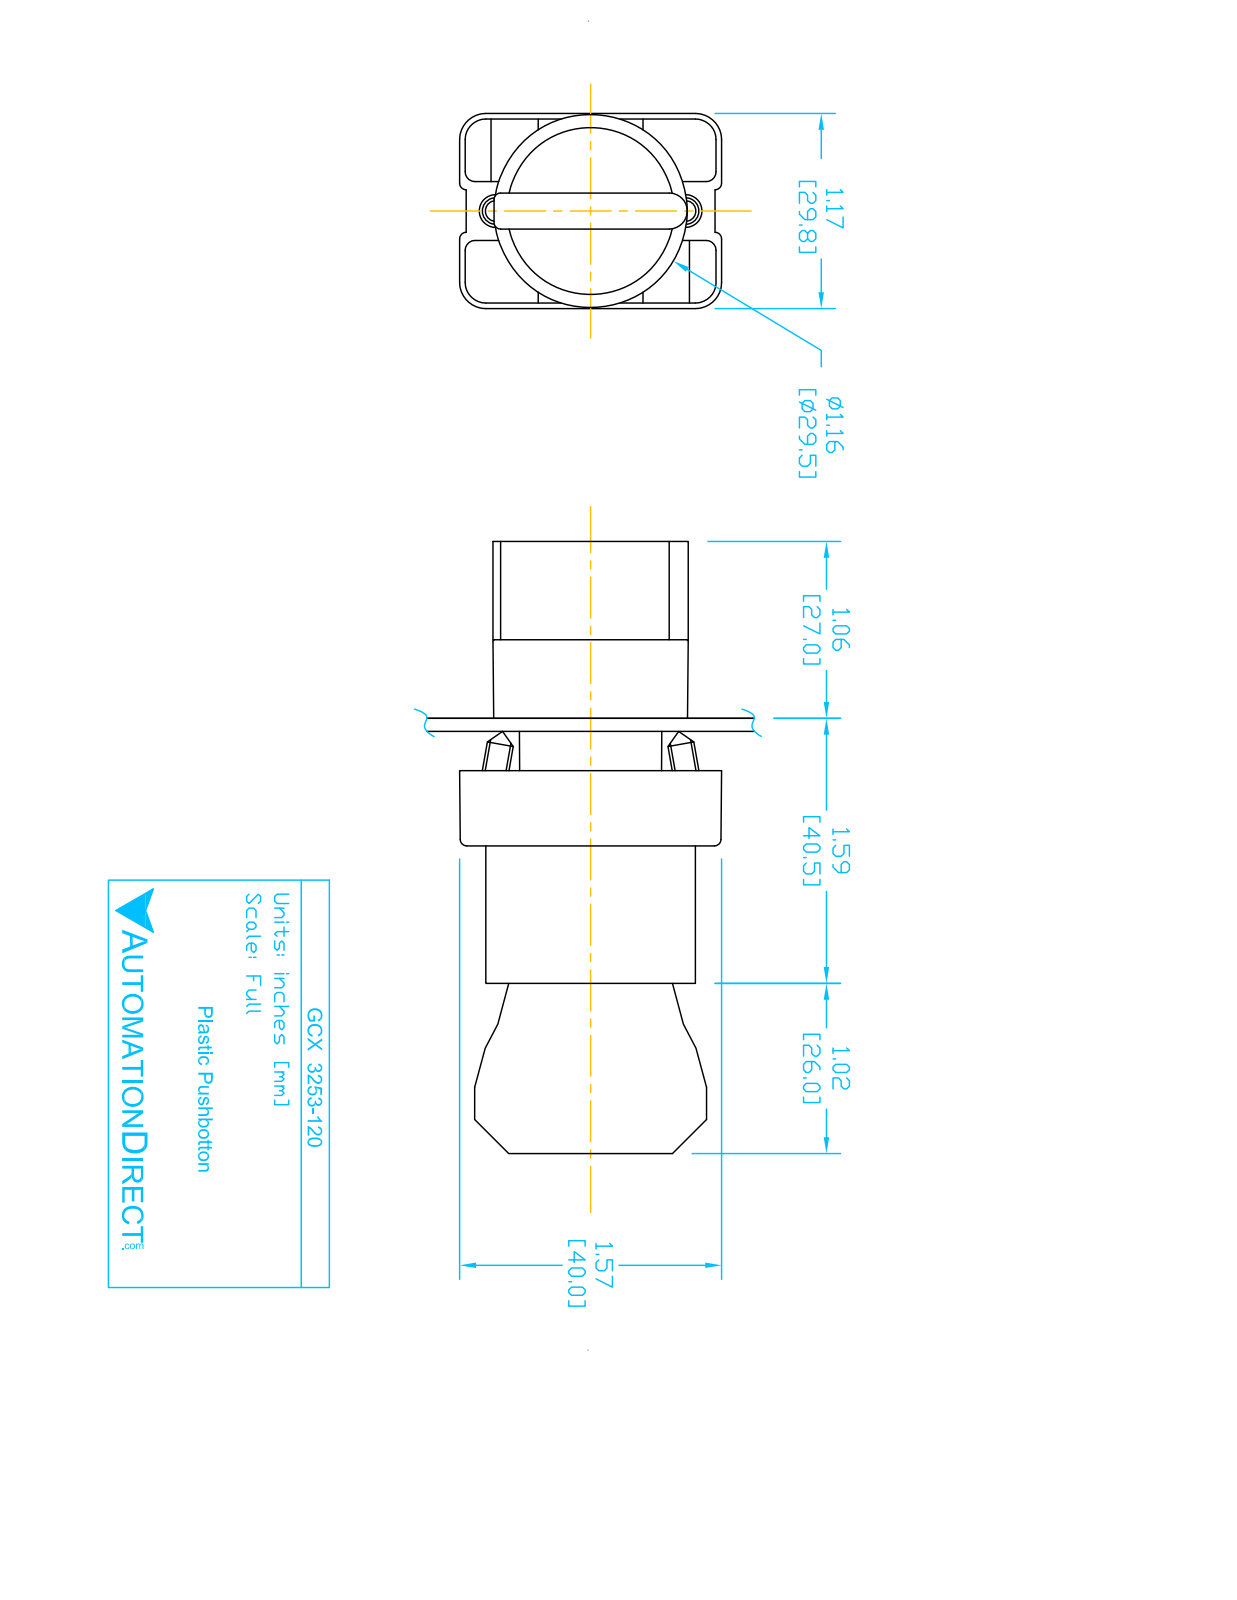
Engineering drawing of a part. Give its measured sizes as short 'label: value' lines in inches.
name: ECX3029-2; ECX1050; GCX3253-120; ecx1040 (+1 more)
written by: SolidWorks 2016 (AUTOMOTIVE_DESIGN)
unit: in
bodies: 8 solids, 445 faces (263 planar, 151 cylindrical, 31 other)
size: 3.653 × 1.581 × 1.177
volume: 2.799 in³; area: 39 in²
holes: 2× ⌀0.079, 2× ⌀0.124, 2× ⌀0.13, 1× ⌀0.087, 1× ⌀0.197, 1× ⌀0.469, 1× ⌀0.878, 1× ⌀0.888, 1× ⌀1.024
bosses: 4× ⌀0.157, 1× ⌀1.175, 1× ⌀1.004, 1× ⌀0.945, 1× ⌀0.856, 1× ⌀0.78, 1× ⌀0.504
rounds: 24× R0.059, 12× R0.041, 12× R0.124, 12× R0.157, 9× R0.039, 2× R0.128, 1× R0.02, 1× R0.063
face distances: 0.827, 2.02, 1.193, 0.579, 1.244, 1.171, 0.472, 0.469, 0.031, 0.033
hole spacings: 0.236, 0.544, 0.472, 0.49
